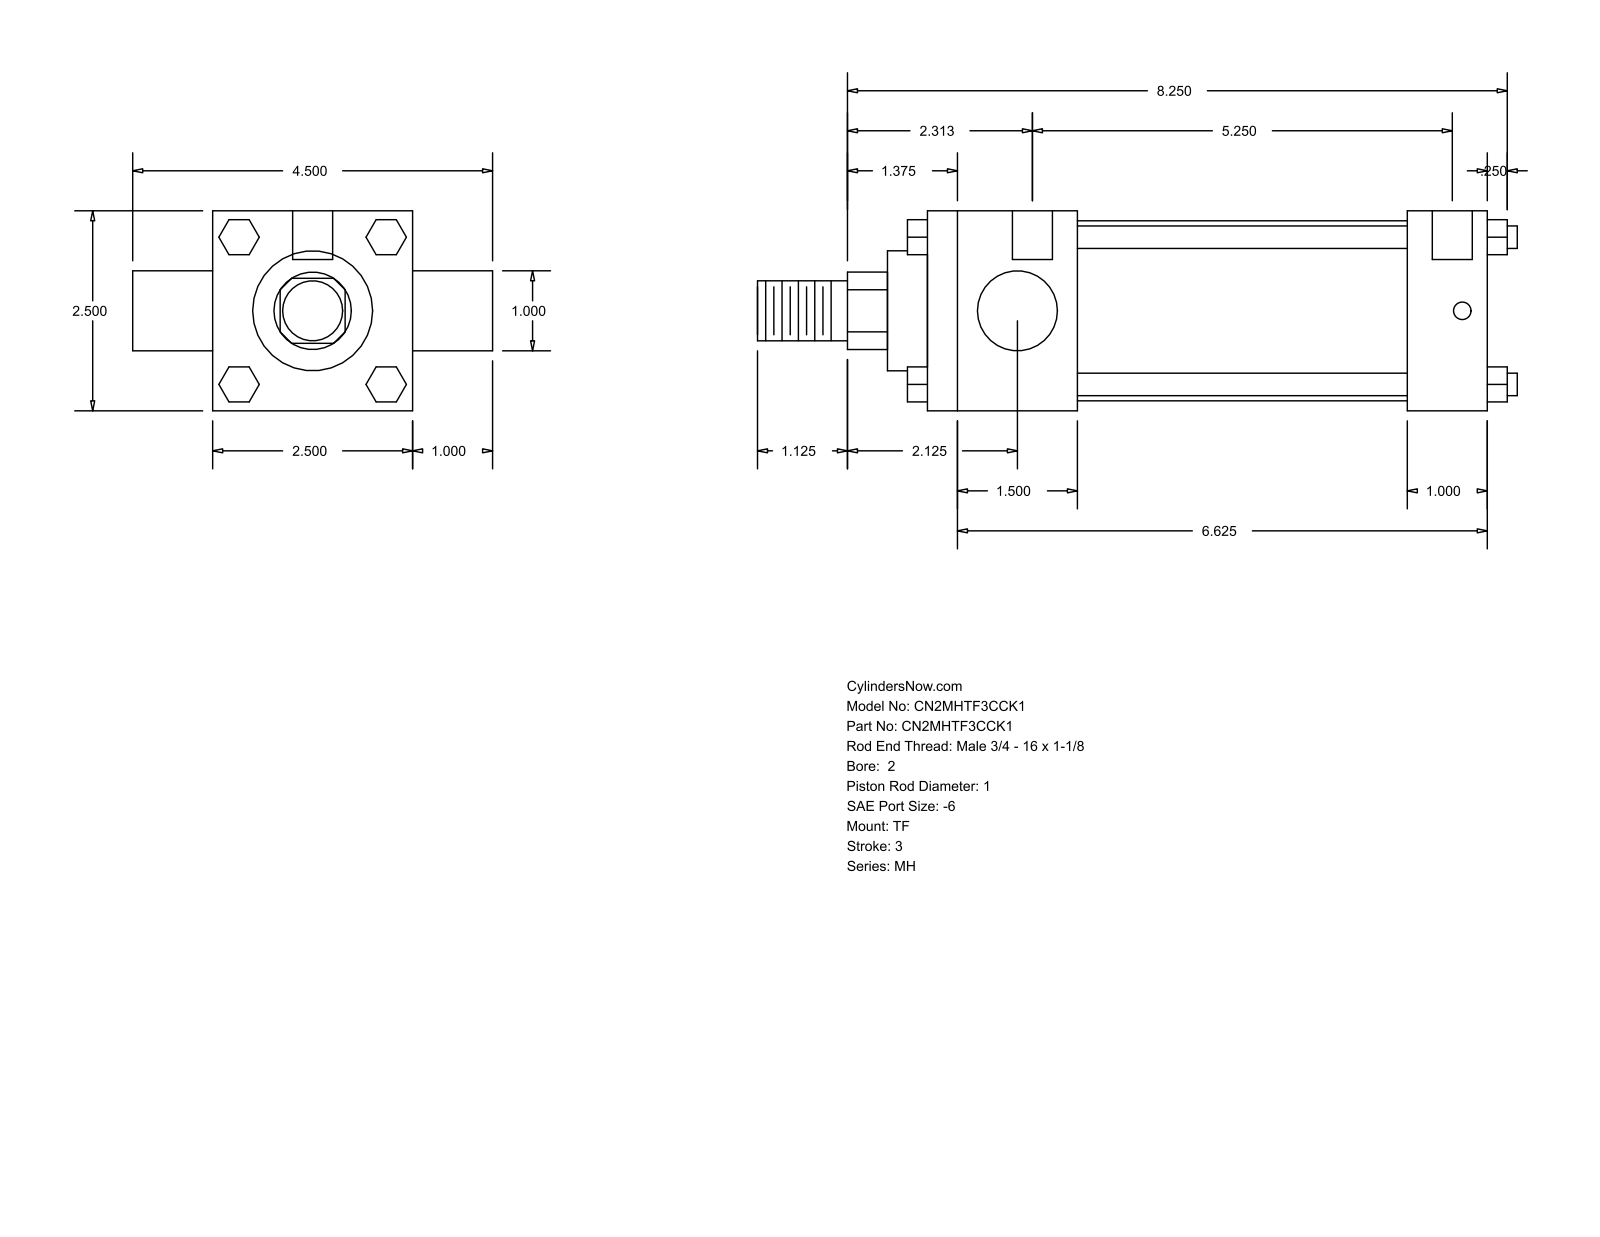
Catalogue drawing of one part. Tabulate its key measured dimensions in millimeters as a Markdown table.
| quantity | value |
| --- | --- |
| part name | MH_TF__0200_1 |
| STEP written by | GSSL Pune (CONFIG_CONTROL_DESIGN) |
| units | millimeters |
| bodies | 0 solids, 120 faces (92 planar, 28 cylindrical, 0 other) |
| overall size | 241.3 × 114.3 × 63.5 |
| round holes (diameter × count) | 5.56 × 3, 12.7 × 2 |
| round bosses / shafts (diameter × count) | 7.14 × 4, 25.4 × 2, 57.15 × 1, 38.1 × 1, 19.05 × 1 |
| partial cylindrical surfaces (radius × count) | 12.29 × 1 |
| main face-to-face distances | 63.5, 177.8, 25.4, 47.63, 152.4, 104.77, 130.17, 88.9, 190.5, 6.35 |
| hole center spacings | 3.17, 4.76, 133.35, 136.52, 138.11, 141.28 |
